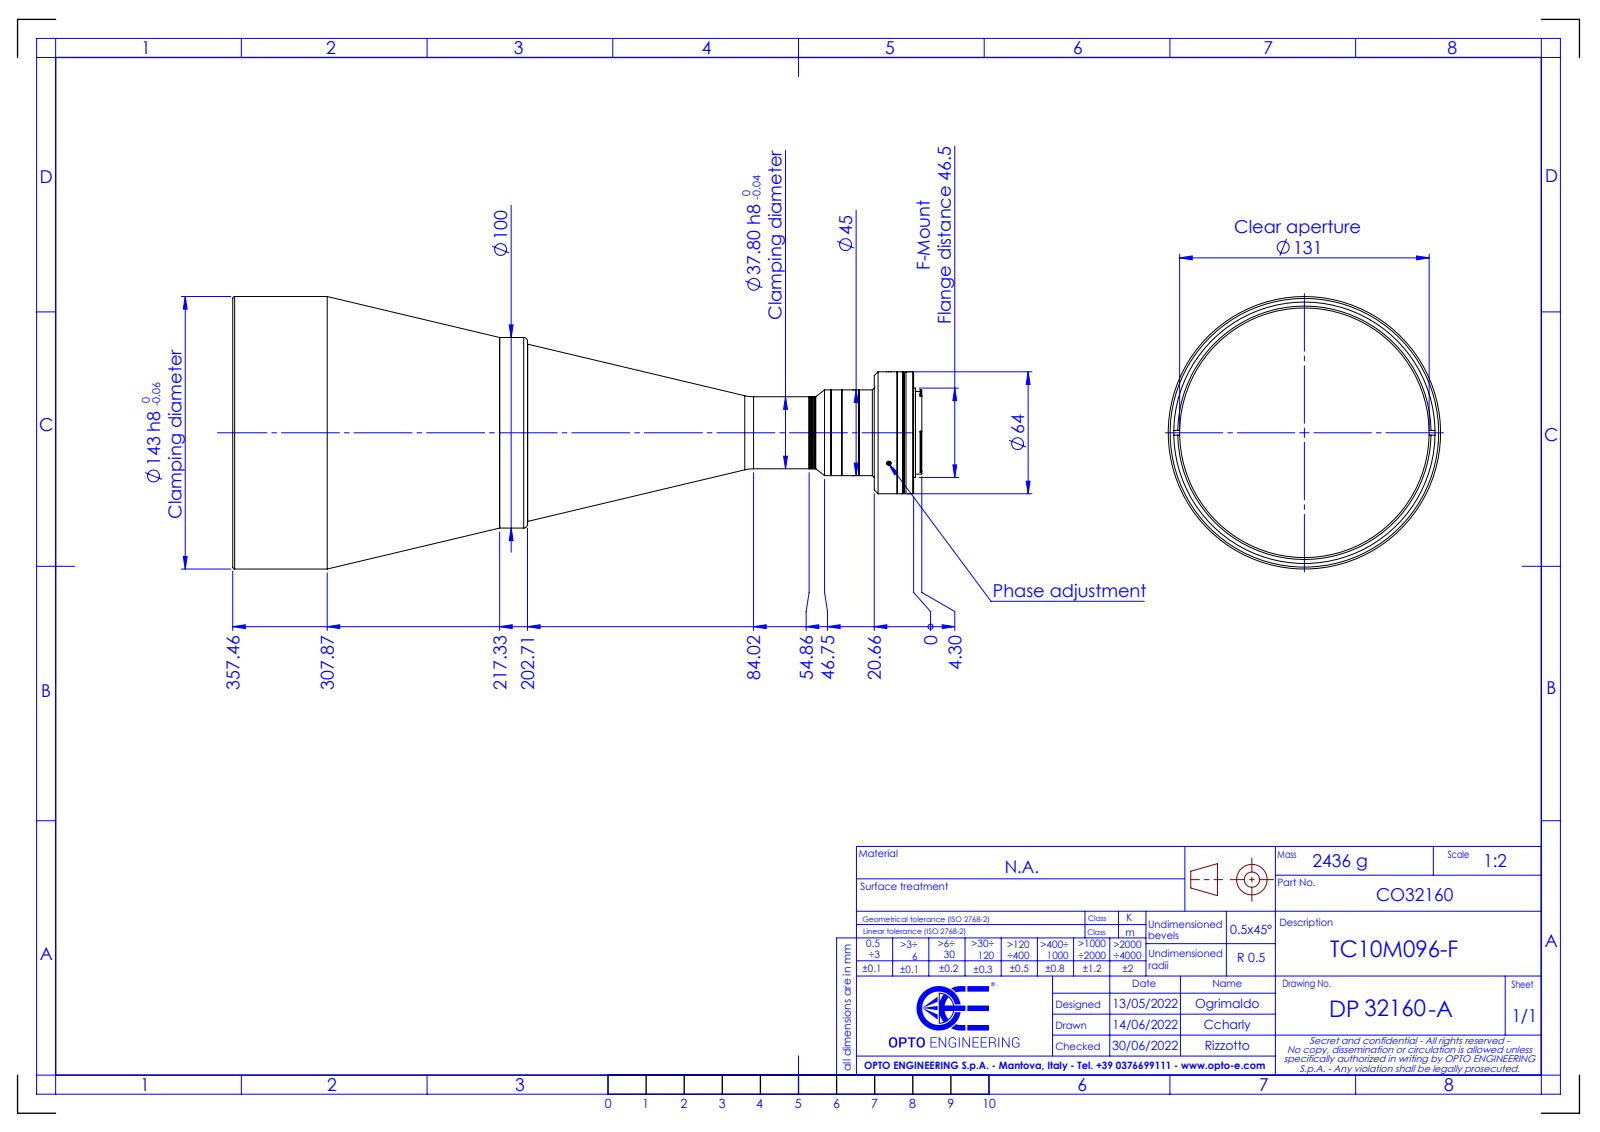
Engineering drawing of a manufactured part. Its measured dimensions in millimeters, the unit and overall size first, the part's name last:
Units: millimetres
Overall size (bounding box): 361.76 × 143 × 143
Round holes (diameter × count): ⌀2.5 ×3, ⌀33 ×1, ⌀42 ×1, ⌀131 ×1, ⌀137.2 ×1
Round bosses / shafts (diameter × count): ⌀143 ×1, ⌀100 ×1, ⌀93 ×1, ⌀64 ×1, ⌀63.5 ×1, ⌀46.9 ×1, ⌀45 ×1, ⌀43.4 ×1
Partial cylindrical surfaces — rounded edges, fillets, slot ends (radius × count): R1.15 ×2, R0.5 ×1, R22.65 ×1
Main face-to-face distances: 139.41, 337.58, 198.17, 356.74, 217.33, 19.16, 1, 5, 1.5, 351.1
Bodies: 0 solids, 122 faces (31 planar, 63 cylindrical, 28 other)
Part name (STEP PRODUCT): DP32160-A_TC10M096-F
STEP written by: SolidWorks 2021 (CONFIG_CONTROL_DESIGN)
